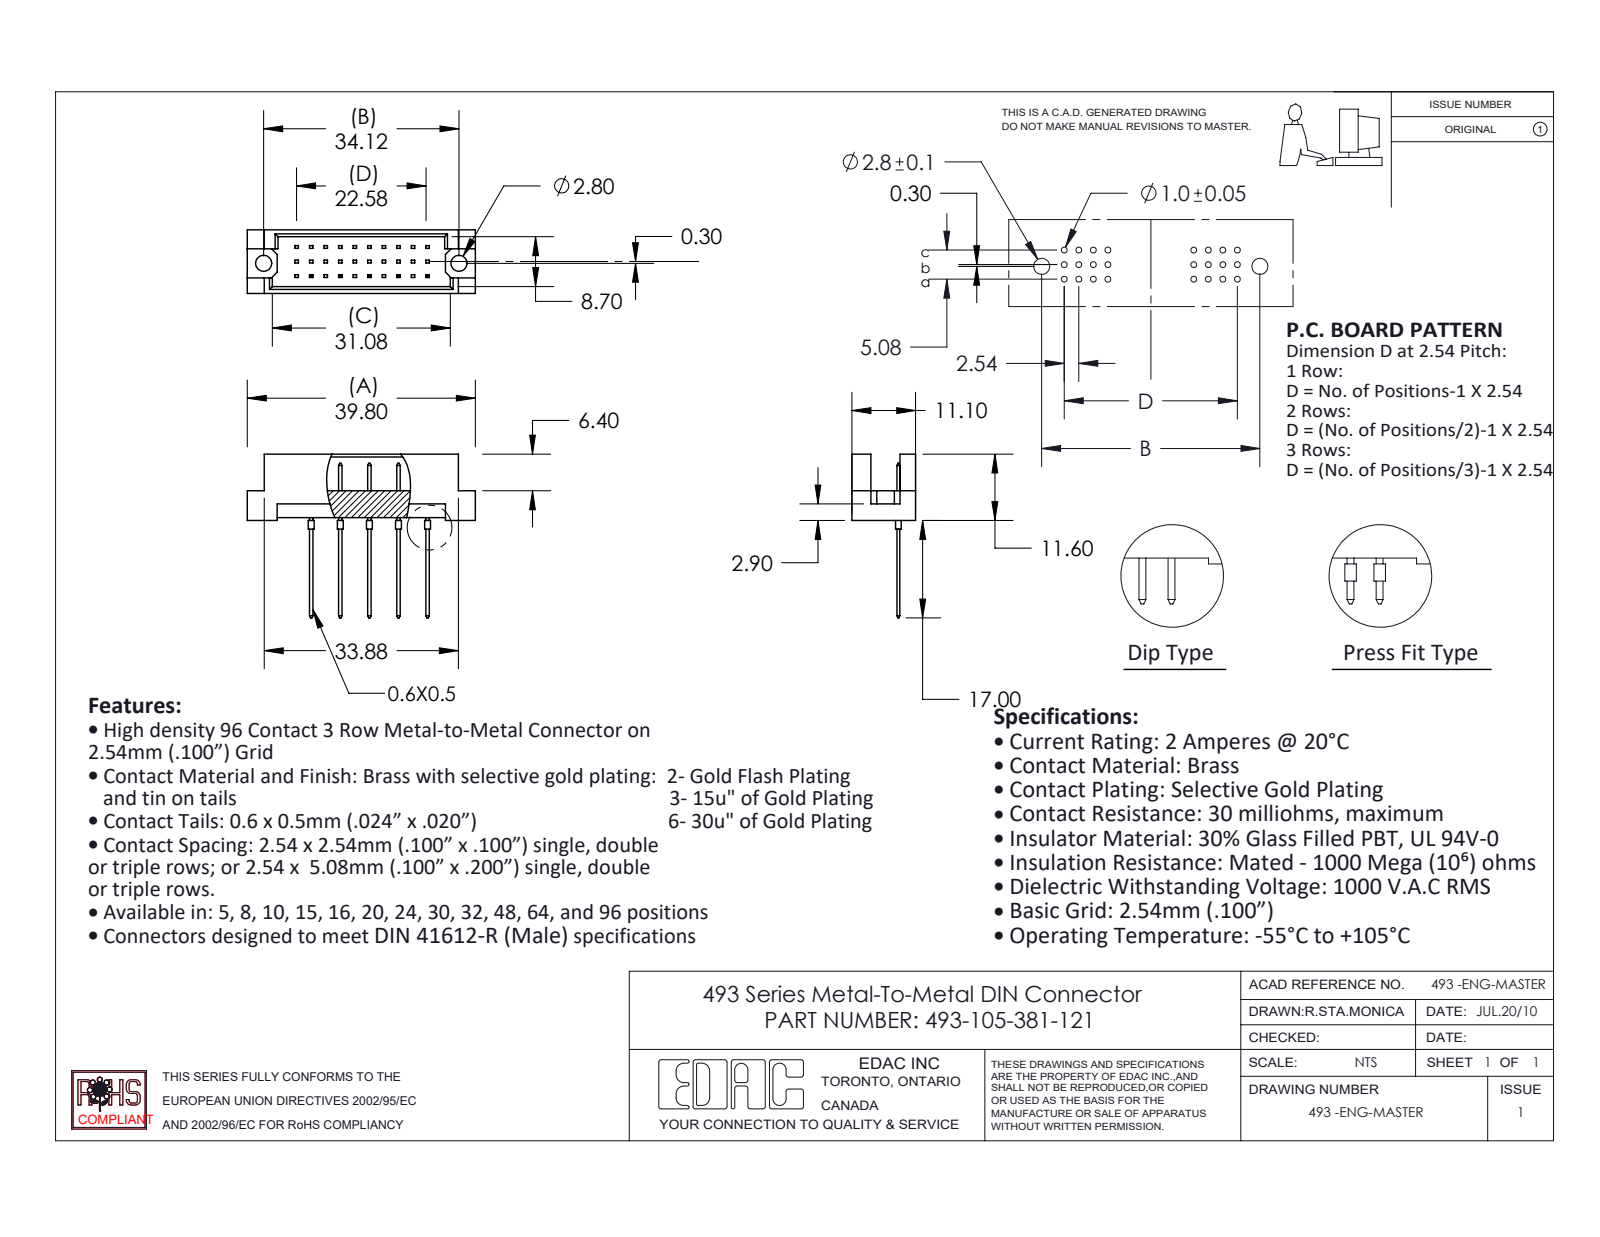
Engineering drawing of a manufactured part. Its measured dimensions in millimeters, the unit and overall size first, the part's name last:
Units: millimetres
Overall size (bounding box): 39.8 × 28.6 × 11.1
Round holes (diameter × count): ⌀2.8 ×2
Round bosses / shafts (diameter × count): ⌀1 ×5
Main face-to-face distances: 1.2, 9.9, 11.1, 8.7, 0.5, 5.08, 4.7, 2.4, 2.76, 8.34
Hole centre spacings: 34.12
Volume: 2 417 mm³ · Surface area: 3 045 mm²
Bodies: 6 solids, 282 faces (268 planar, 14 cylindrical, 0 other)
Part name (STEP PRODUCT): 493-290_81; 493-105-381-121; 493 Part_30
STEP written by: SolidWorks 2020 (CONFIG_CONTROL_DESIGN)
